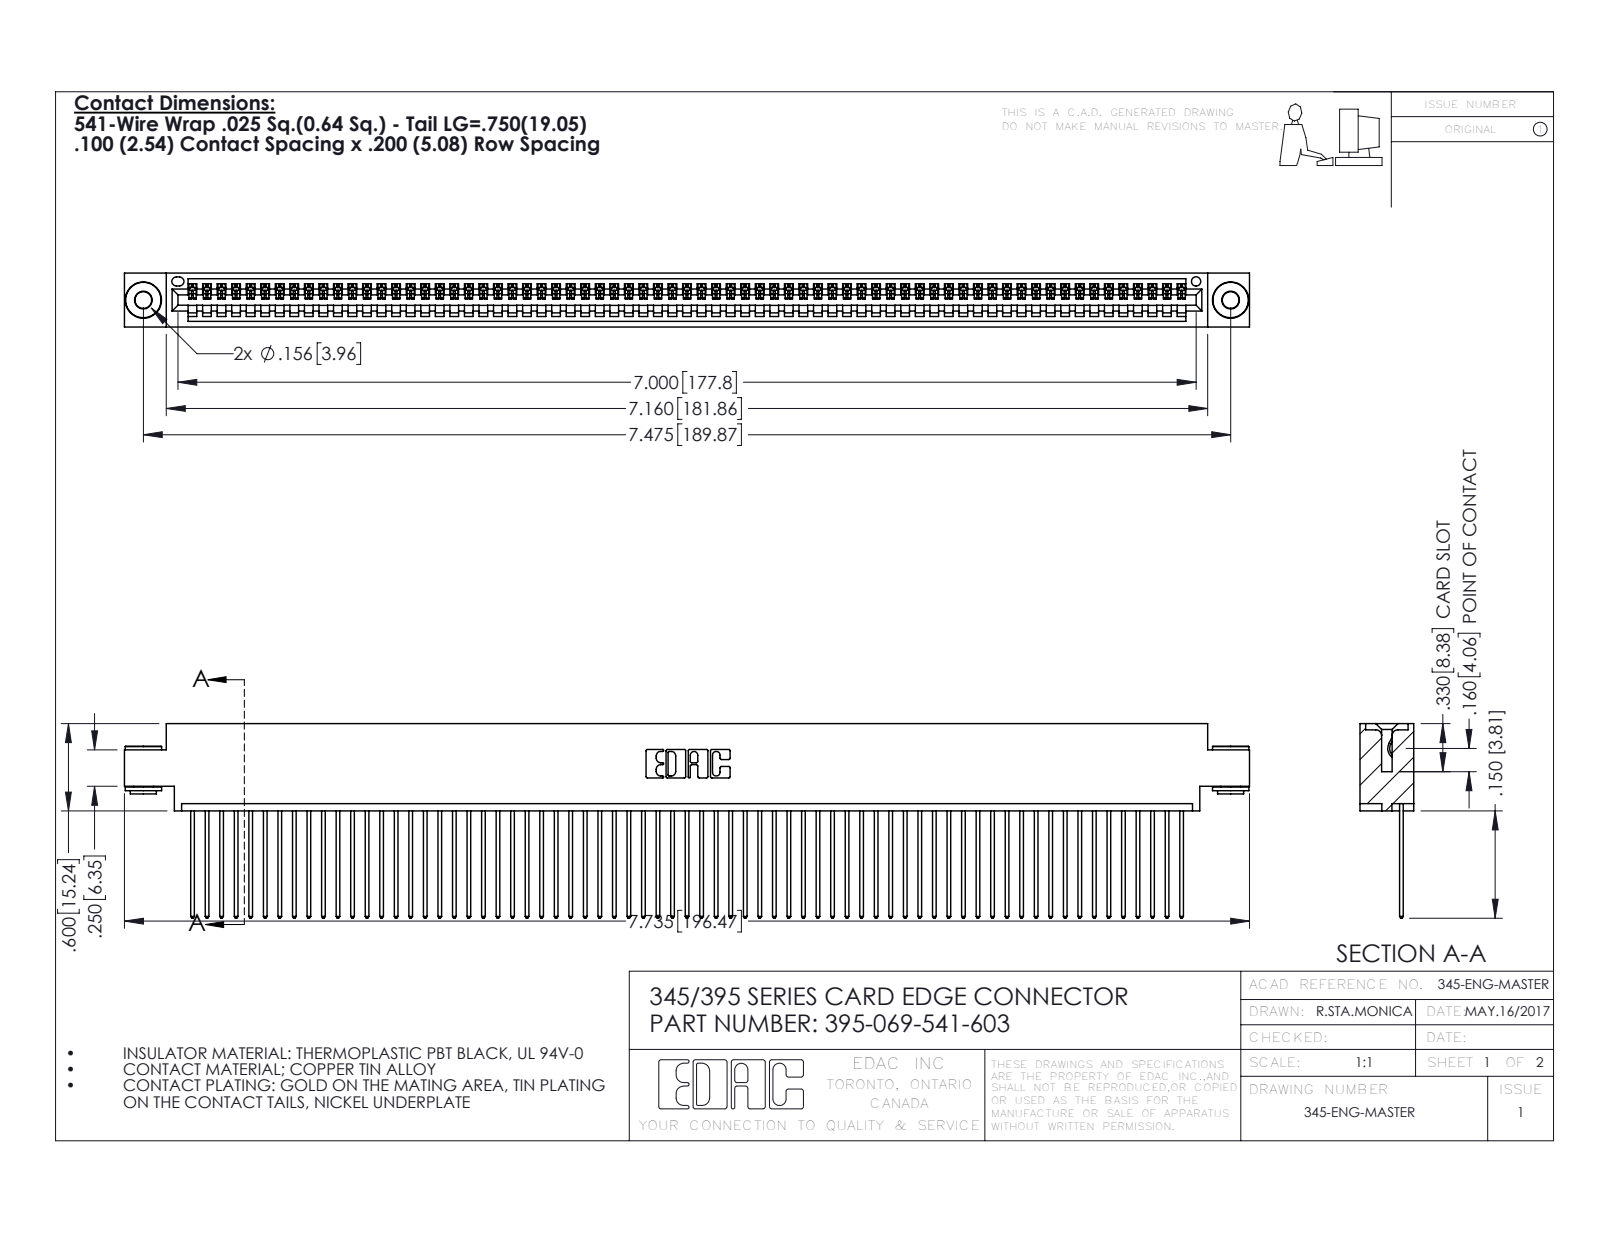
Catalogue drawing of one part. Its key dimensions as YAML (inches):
part_name: "395-069-541-603; 345 Part_0.170 Offset - 0.156 Dia-TH; 345-292-001_345-293-141; 345-250-002_345-250-002-102"
step_written_by: "SolidWorks 2016 (CONFIG_CONTROL_DESIGN)"
units: inches
bodies: {solids: 72, faces: 4170, planar: 2854, cylindrical: 1308, other: 8}
overall_size: [7.735, 1.337, 0.37]
volume: 1.16
surface_area: 42.34
round_holes:
  - {diameter: 0.116, count: 2}
  - {diameter: 0.156, count: 2}
  - {diameter: 0.064, count: 1}
round_bosses_or_shafts:
  - {diameter: 0.25, count: 2}
  - {diameter: 0.18, count: 2}
  - {diameter: 0.136, count: 2}
partial_cylinders:
  - {radius: 0.006, count: 138}
  - {radius: 0.01, count: 138}
  - {radius: 0.01, count: 22}
  - {radius: 0.007, count: 6}
  - {radius: 0.031, count: 6}
  - {radius: 0.026, count: 3}
  - {radius: 0.031, count: 2}
  - {radius: 0.04, count: 2}
face_to_face_distances: [0.072, 0.298, 0.098, 0.272, 0.025, 0.37, 0.2, 0.225, 0.175, 0.149]
hole_center_spacings: [0.27, 7.239, 7.475]
